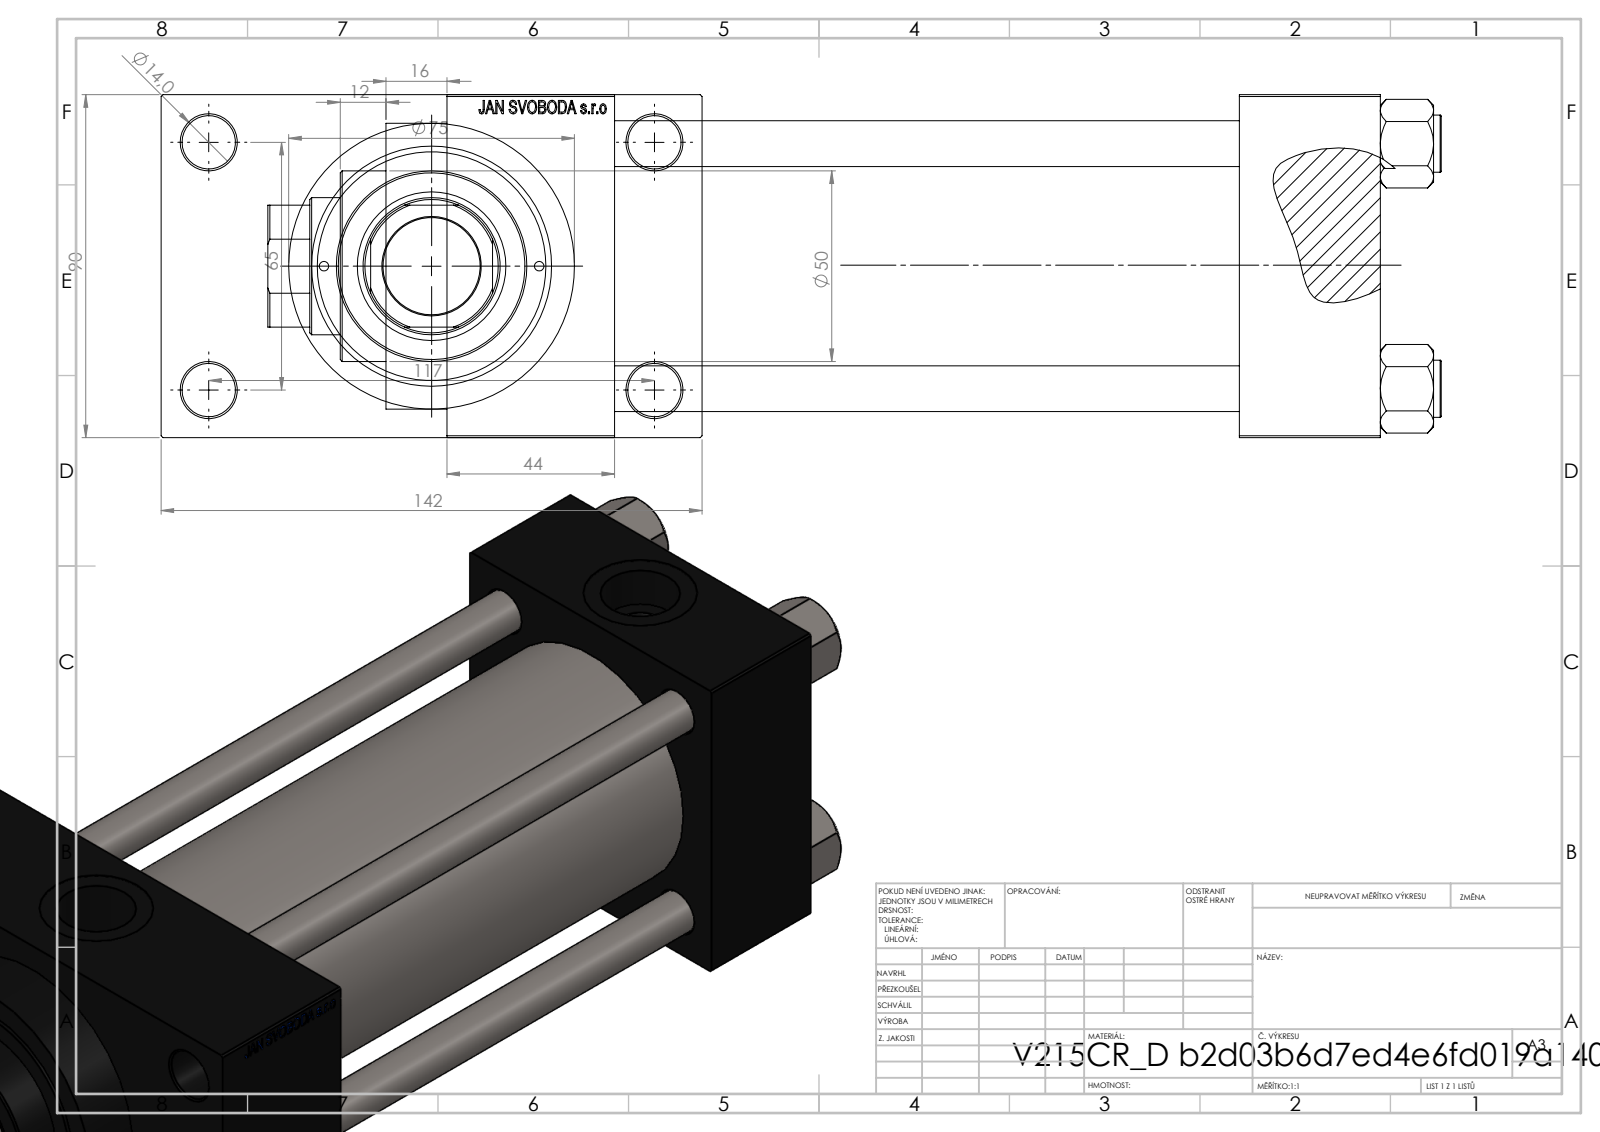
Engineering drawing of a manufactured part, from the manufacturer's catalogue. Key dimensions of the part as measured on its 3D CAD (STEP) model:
Part name (STEP PRODUCT): V215CR_D_Body; NUT_M5_D; V215CR_VCP_D; V215CR_D_TYCINKA (+1 more)
STEP written by: SolidWorks 2019 (CONFIG_CONTROL_DESIGN)
Units: millimetres
Bodies: 11 solids, 1112 faces (499 planar, 93 cylindrical, 520 other)
Overall size (bounding box): 308 × 142 × 90
Volume: 1 340 000 mm³ · Surface area: 275 244 mm²
Round holes (diameter × count): ⌀12 ×4, ⌀14 ×4, ⌀2.5 ×2, ⌀7 ×2, ⌀20.96 ×2, ⌀30 ×2, ⌀25.5 ×1, ⌀36 ×1, ⌀39 ×1, ⌀50 ×1, ⌀60 ×1, ⌀63 ×1
Round bosses / shafts (diameter × count): ⌀15 ×4, ⌀75 ×1, ⌀69 ×1
Partial cylindrical surfaces — rounded edges, fillets, slot ends (radius × count): R17.5 ×1
Main face-to-face distances: 90, 164, 37, 201, 245, 208, 44, 26, 116, 142
Hole centre spacings: 26.35, 32.39, 44.4, 45.47, 64.3, 66.92, 68.42, 69.81
